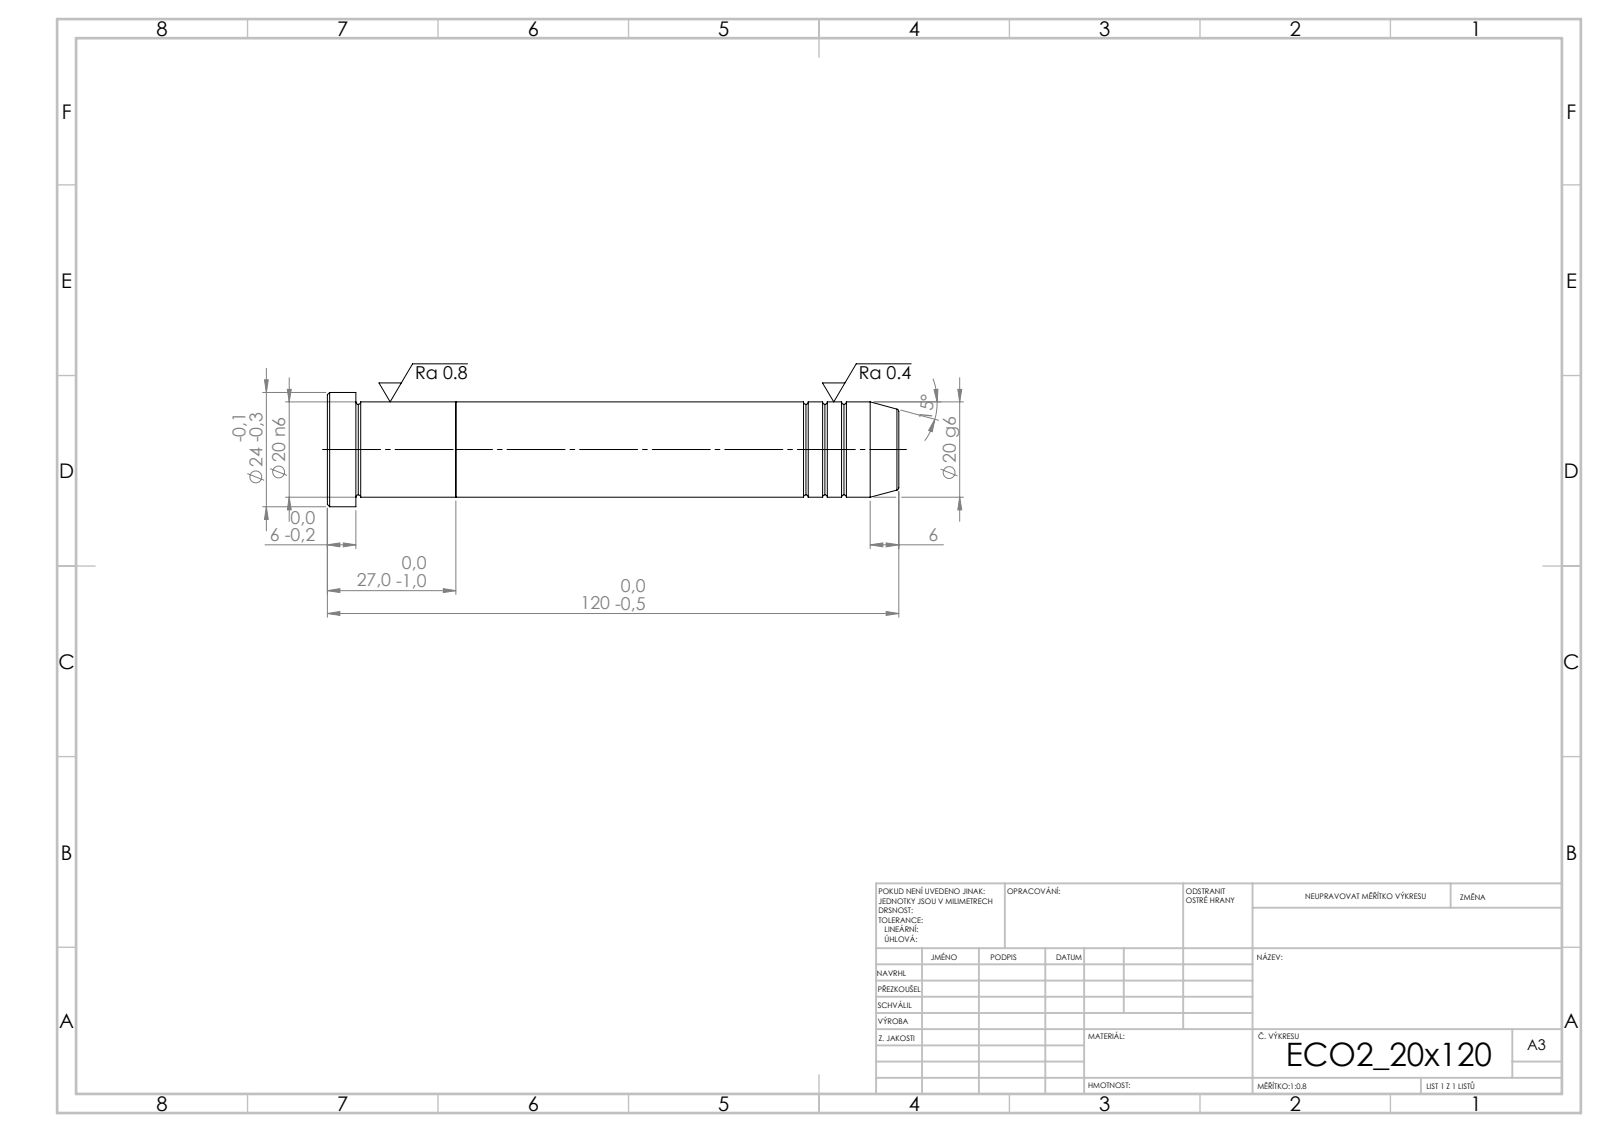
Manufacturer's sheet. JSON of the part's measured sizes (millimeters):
{"step_written_by": "SolidWorks 2019 (CONFIG_CONTROL_DESIGN)", "units": "millimeters", "bodies": {"solids": 2, "faces": 39, "planar": 5, "cylindrical": 12, "other": 22}, "overall_size": [120, 24, 24], "volume_mm3": 38134, "surface_area_mm2": 9140, "round_bosses_or_shafts": [[24, 1], [20, 1]], "face_to_face_distances": [27, 93, 120, 114, 21, 6]}
